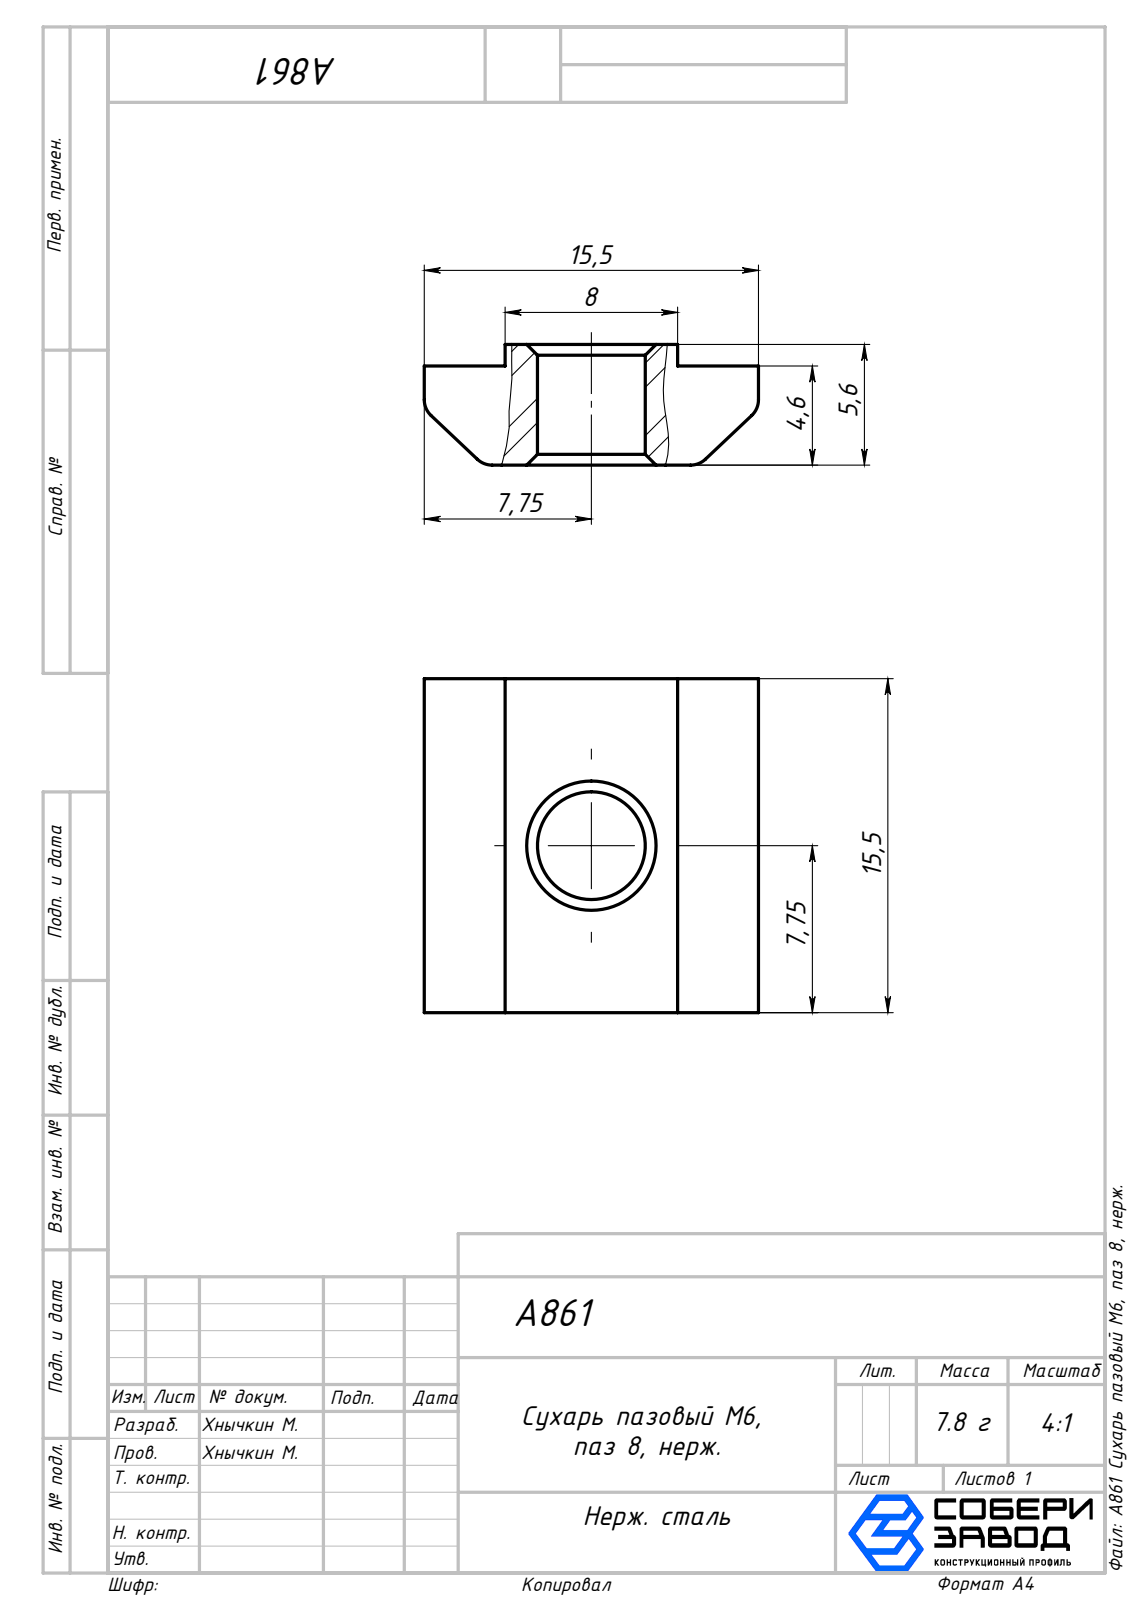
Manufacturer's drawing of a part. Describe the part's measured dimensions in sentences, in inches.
The part is named "A861 Сухарь пазовый М6, паз 8, нерж.". Its 3-D file was written by "SolidWorks 2025 (AUTOMOTIVE_DESIGN)". It is 1 solid with 22 faces: 12 planar, 6 cylindrical and 4 other. Overall it measures 0.61 by 0.61 by 0.22 inches. Its volume is 0.061 cubic inches and its surface area 1.22 square inches. Round holes: 1 of diameter 0.197. Partial cylindrical surfaces (rounded edges, fillets, slot ends): 4 of radius 0.039. The main face-to-face distances are 0.181, 0.61, 0.22, 0.039, 0.148, 0.463, 0.315.
